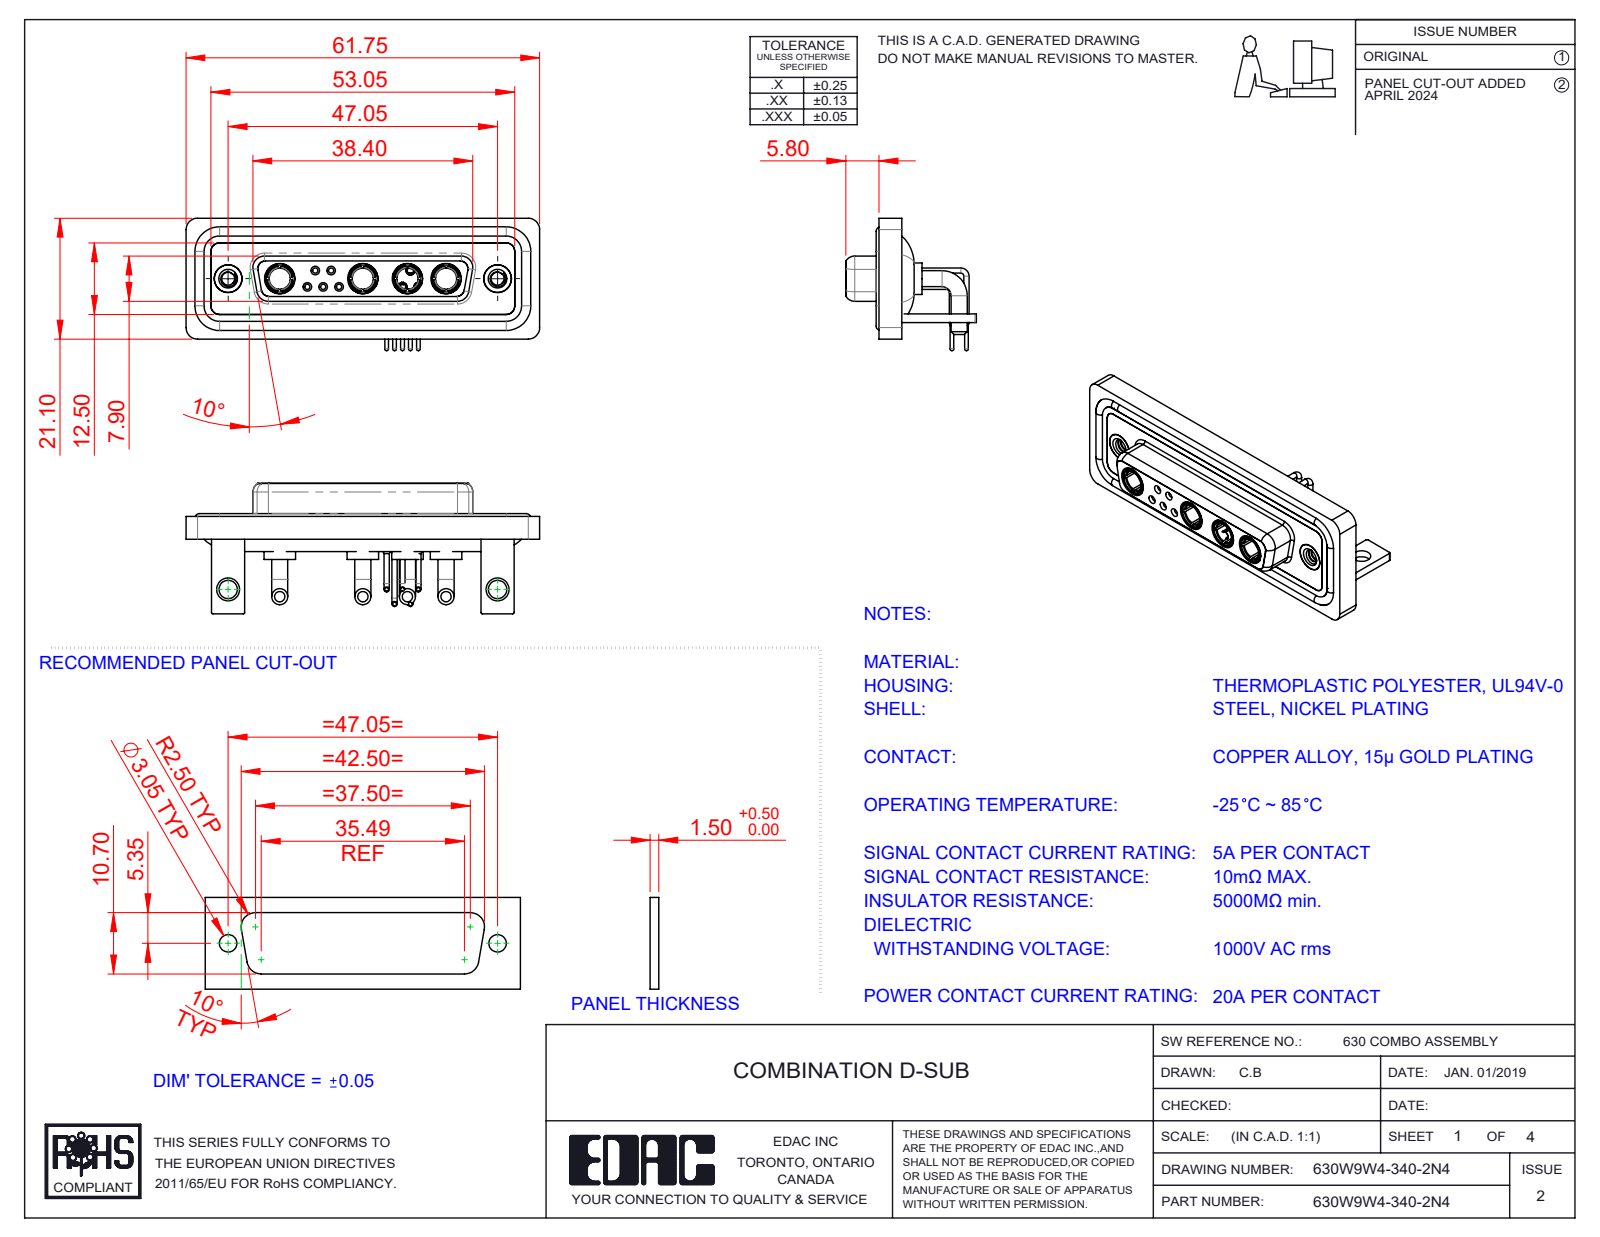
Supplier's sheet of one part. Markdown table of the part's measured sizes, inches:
| quantity | value |
| --- | --- |
| part name | 630Combo Shell Rear_25 Contacts; 630Combo Waterproof Housing_25 Contacts; 630Combo Shell Front_25 Contacts; 630Combo Stabilizer Bracket_50 Contacts (+6 more) |
| STEP written by | SolidWorks 2023 (CONFIG_CONTROL_DESIGN) |
| units | inches |
| bodies | 22 solids, 1011 faces (316 planar, 427 cylindrical, 268 other) |
| overall size | 2.431 × 0.91 × 0.898 |
| volume | 0.538 in³ |
| surface area | 22.91 in² |
| round holes (diameter × count) | 0.191 × 6, 0.035 × 5, 0.043 × 5, 0.059 × 5, 0.079 × 5, 0.146 × 4, 0.209 × 4, 0.063 × 3, 0.067 × 2, 0.089 × 2, 0.126 × 2, 0.157 × 2 |
| round bosses / shafts (diameter × count) | 0.035 × 10, 0.063 × 9, 0.11 × 8, 0.079 × 5, 0.059 × 5, 0.026 × 5, 0.217 × 4, 0.205 × 4 |
| partial cylindrical surfaces (radius × count) | 0.079 × 19, 0.059 × 18, 0.01 × 16, 0.053 × 8, 0.063 × 8, 0.02 × 5, 0.024 × 4, 0.026 × 4 |
| main face-to-face distances | 0.016, 0.071, 0.114, 0.146, 0.059, 0.161, 0.043, 0.055, 0.063, 0.098 |
| hole center spacings | 0.124, 0.109, 0.198, 0.545, 0.436, 0.504, 0.61, 0.218 |
